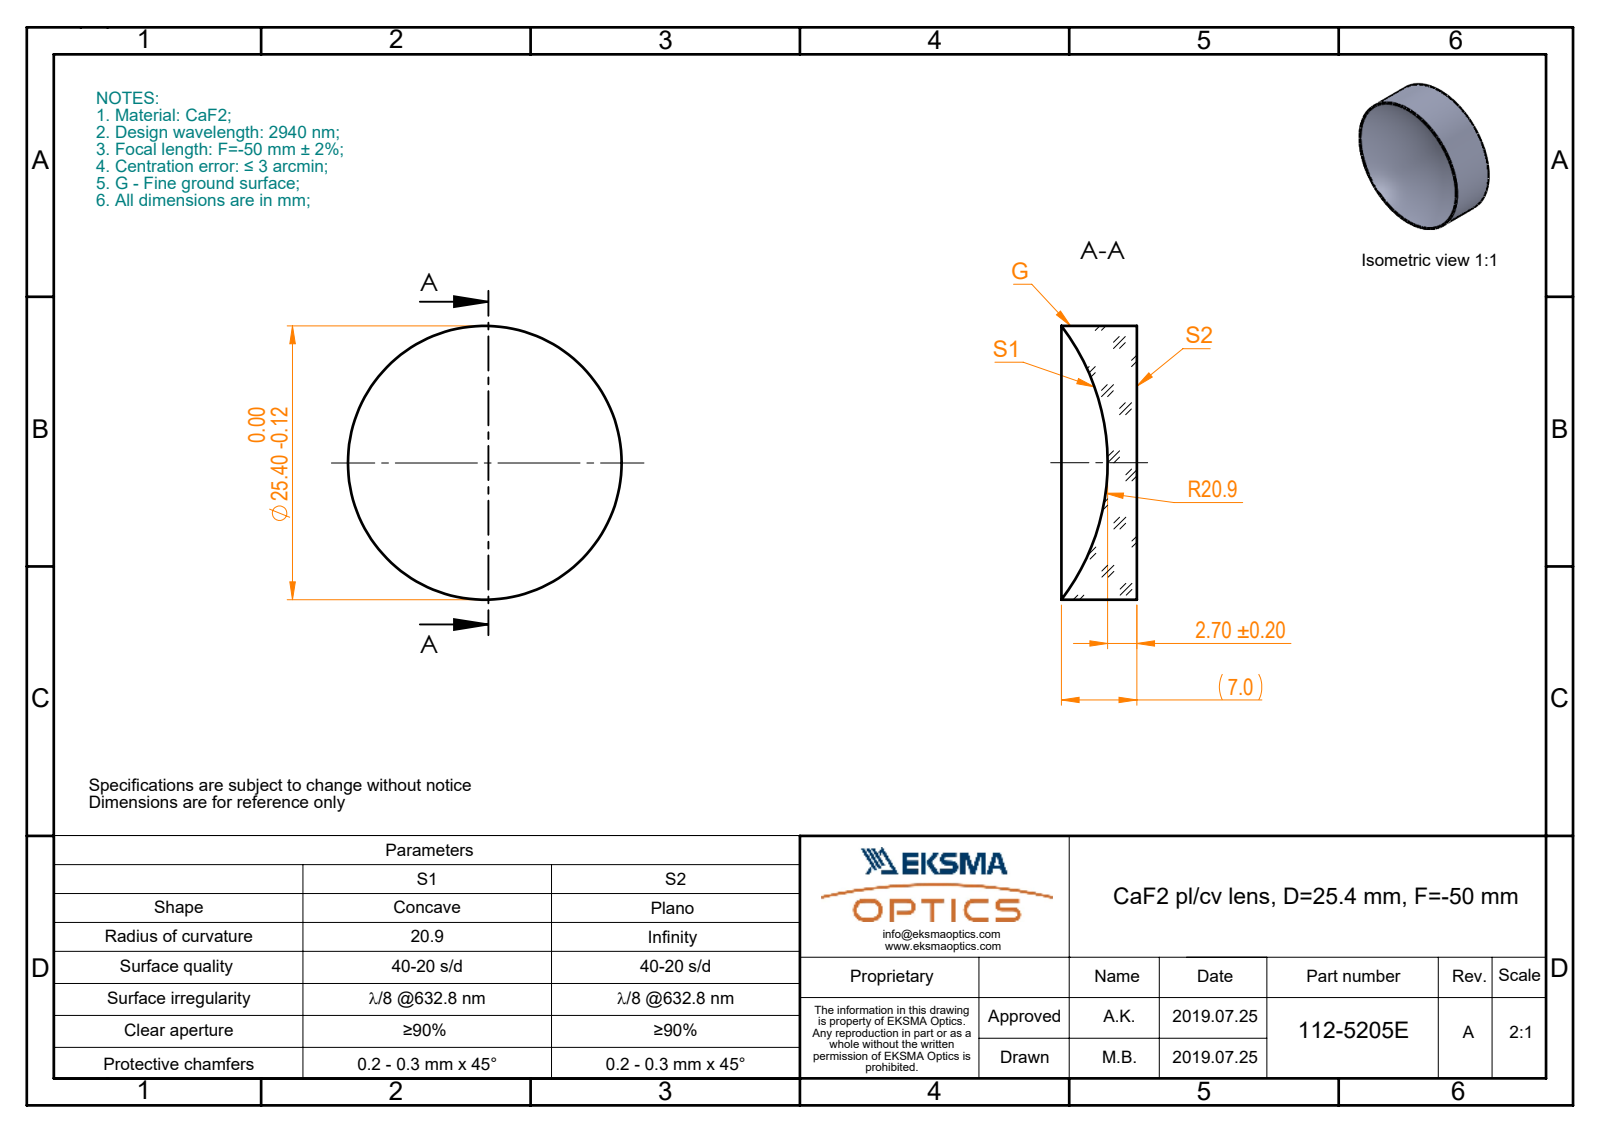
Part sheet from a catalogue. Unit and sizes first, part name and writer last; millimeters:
Units: millimetres
Overall size (bounding box): 25.4 × 25.4 × 7
Round bosses / shafts (diameter × count): ⌀25.4 ×1
Volume: 2 416 mm³ · Surface area: 1 630 mm²
Bodies: 1 solid, 5 faces (1 planar, 2 cylindrical, 2 other)
Part name (STEP PRODUCT): 112-5205E CaF2 pl-cv 12.7 F-50
STEP written by: SolidWorks 2017 (CONFIG_CONTROL_DESIGN)
